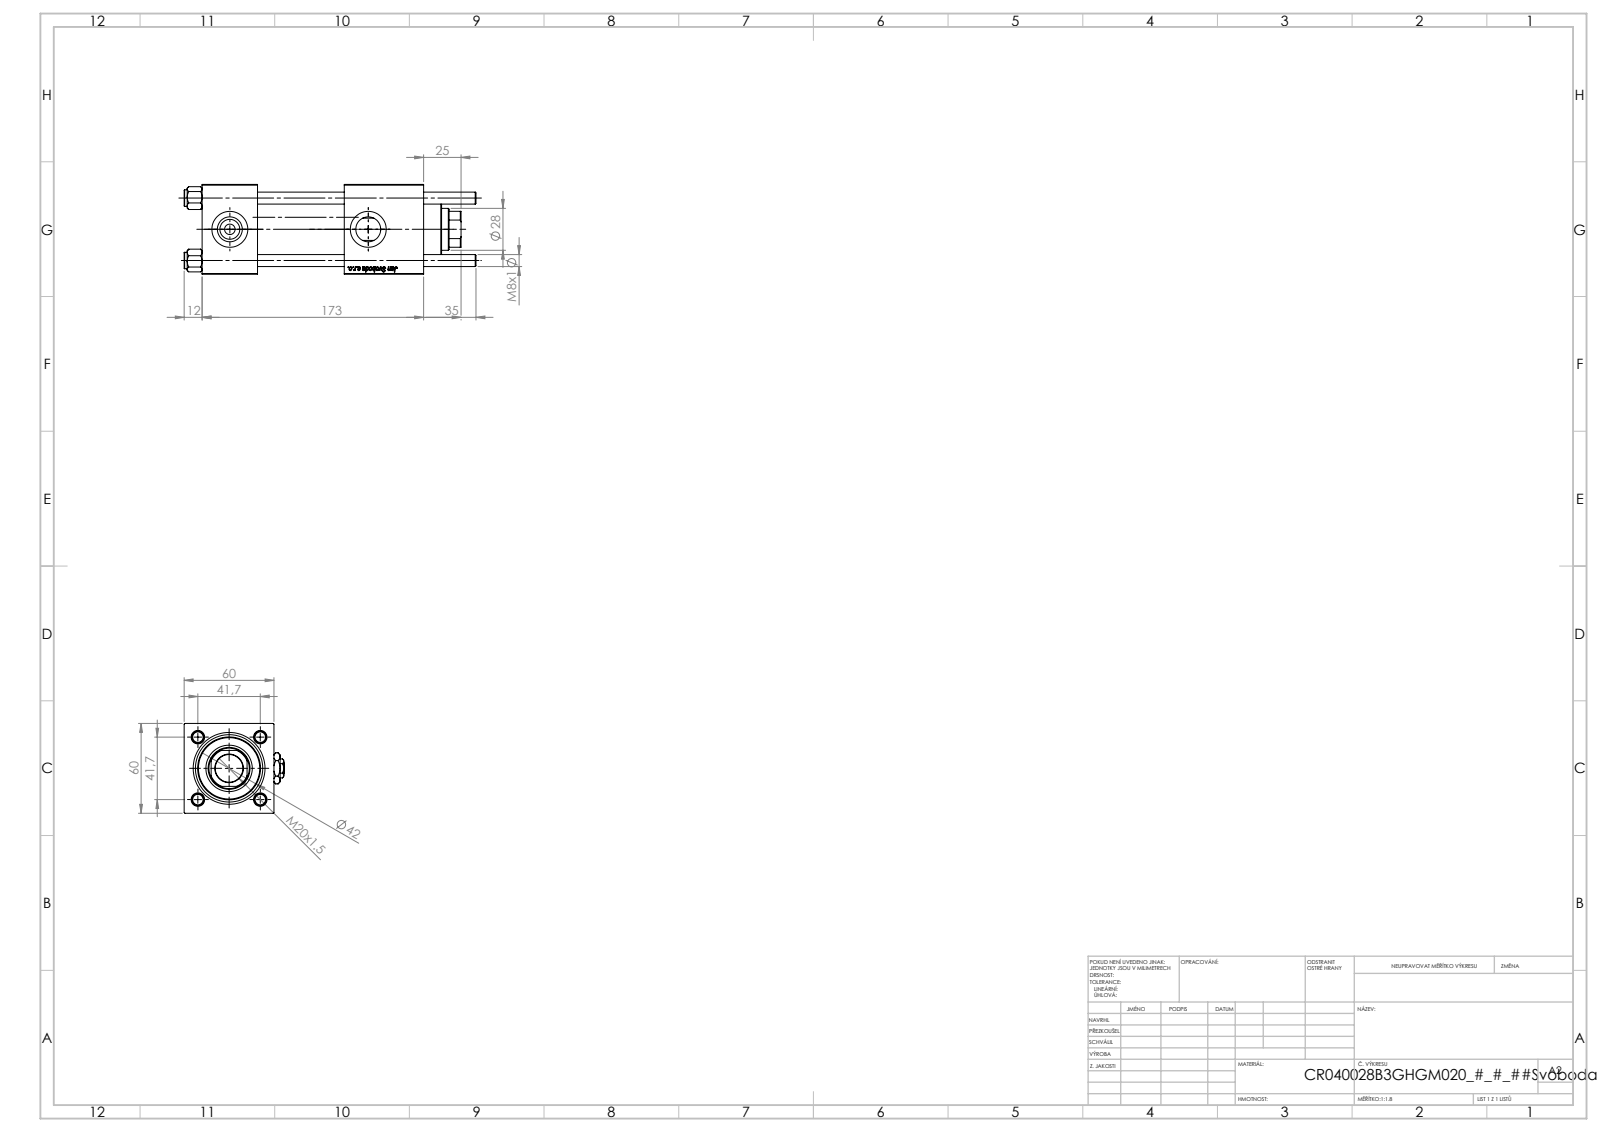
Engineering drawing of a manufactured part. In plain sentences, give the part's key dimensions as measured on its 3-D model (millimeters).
The part is named "V215CR_B-1; V215CR_B_TYCINKA; V215CR_VCP_B; NUT_M5_B (+2 more)". Its 3-D file was written by "SolidWorks 2019 (CONFIG_CONTROL_DESIGN)". It is 13 solids with 1259 faces: 481 planar, 88 cylindrical and 690 other. Overall it measures 195 by 67 by 60 millimeters. Its volume is 432 328 cubic millimeters and its surface area 122 775 square millimeters. Round holes: 4 of diameter 8, 2 of diameter 7, 2 of diameter 16.66, 2 of diameter 24, 1 of diameter 18.5, 1 of diameter 28, 1 of diameter 31, 1 of diameter 40, 1 of diameter 45. Round bosses or shafts: 4 of diameter 11, 1 of diameter 46, 1 of diameter 42. Partial cylindrical surfaces (rounded edges, fillets, slot ends): 1 of radius 13.5. The main face-to-face distances are 60, 37, 58, 95, 53, 119.3, 82.3, 24.3, 148, 111. The hole center spacings are 29.49, 41.7, 58.97, 92.5.
